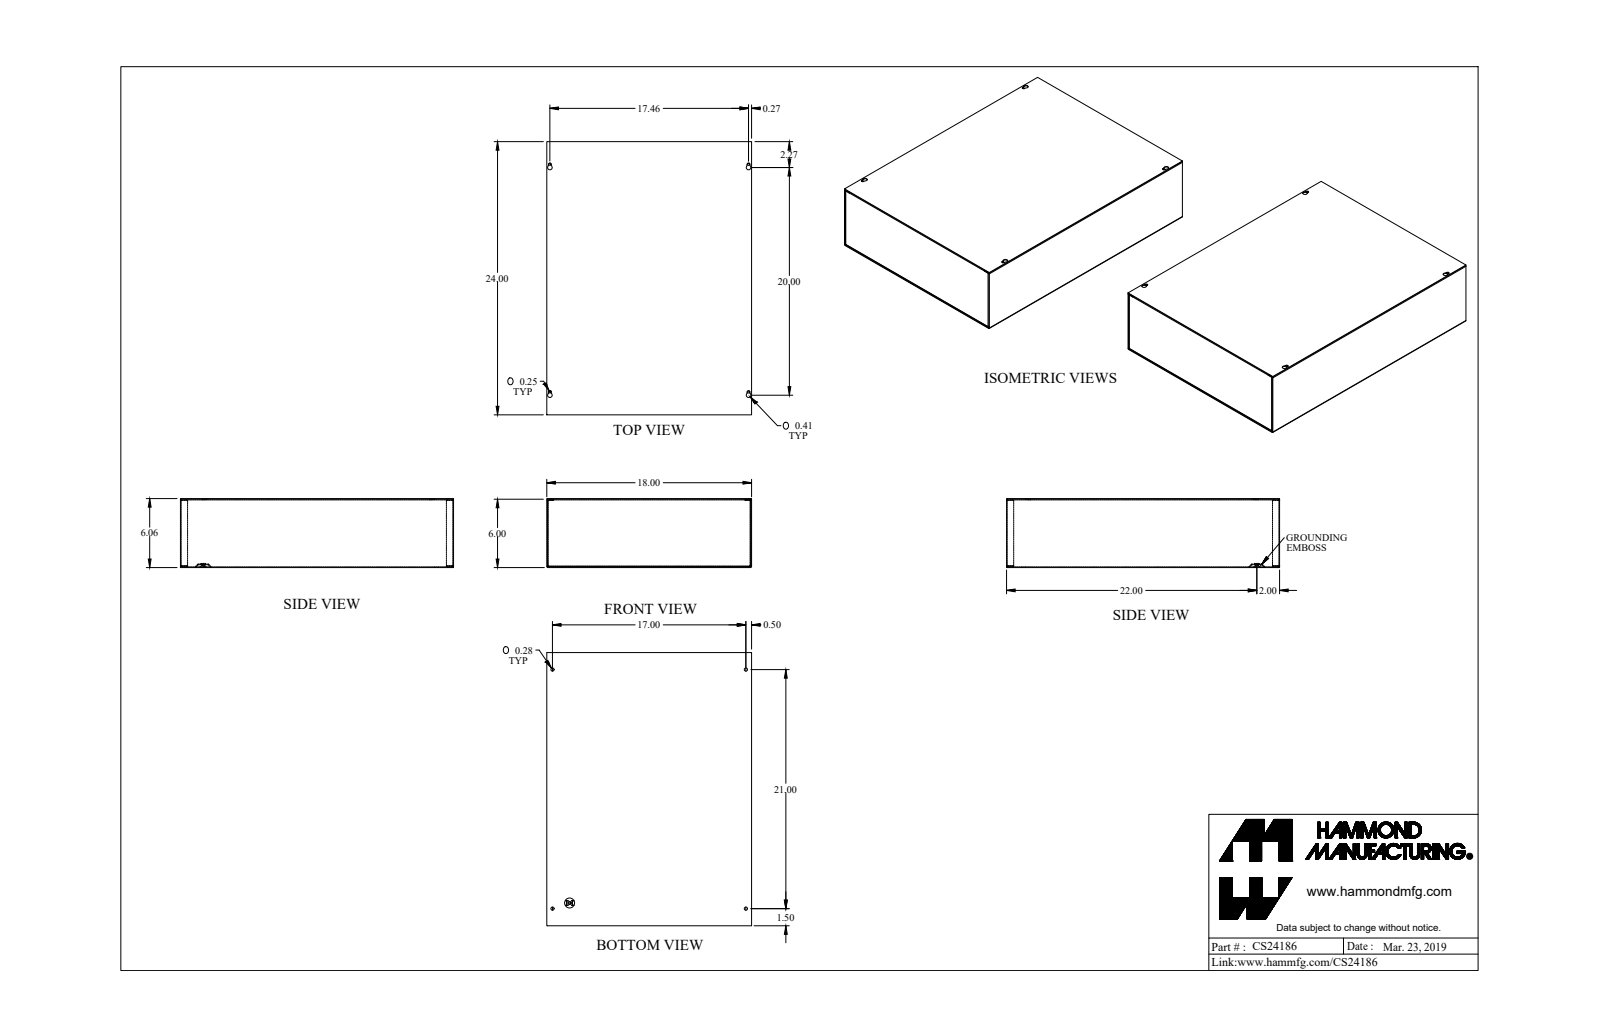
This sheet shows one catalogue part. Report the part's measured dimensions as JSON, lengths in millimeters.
{"part_name": "CS24186_Default", "step_written_by": "SolidWorks 2019 (CONFIG_CONTROL_DESIGN)", "units": "millimeters", "bodies": {"solids": 4, "faces": 205, "planar": 125, "cylindrical": 72, "other": 8}, "overall_size": [609.6, 457.2, 153.8], "volume_mm3": 1331000, "surface_area_mm2": 1850000, "round_holes": [[4.3, 5], [7.1, 4], [12.7, 1]], "round_bosses_or_shafts": [[12.5, 1], [7.2, 1]], "partial_cylinders_radius": [[0.7, 12], [2.2, 12], [1.4, 8], [3.2, 4], [5.2, 4]], "face_to_face_distances": [1.4, 152.4, 151, 153.8, 455.8, 608.2, 457.2, 454.3, 609.6, 606.7], "hole_center_spacings": [14, 437.8, 520.7, 680.2, 431.8, 443.5, 508, 533.4]}
